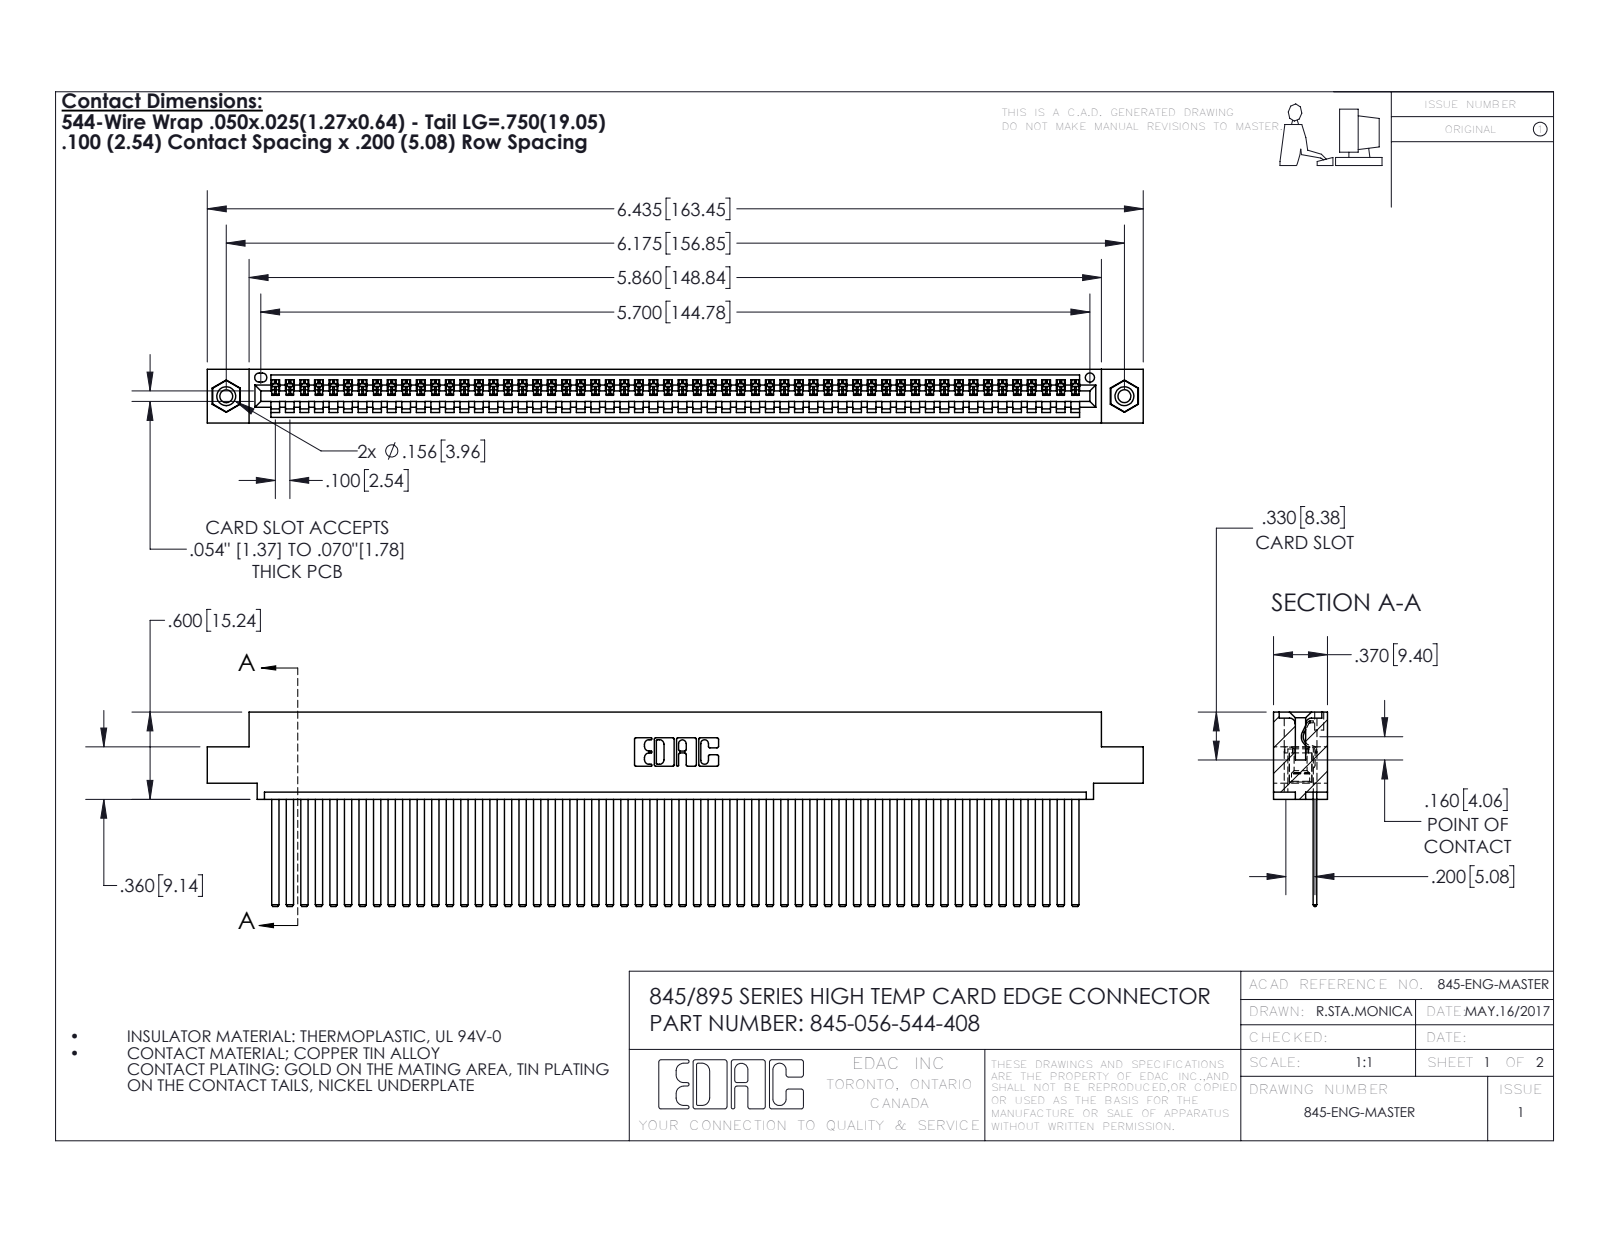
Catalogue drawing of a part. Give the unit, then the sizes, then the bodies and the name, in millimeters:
Units: millimetres
Overall size (bounding box): 163.4 × 34 × 9.4
Round holes (diameter × count): ⌀2.3 ×2, ⌀3.2 ×2, ⌀4 ×2, ⌀1.6 ×1
Round bosses / shafts (diameter × count): ⌀3.9 ×2
Partial cylindrical surfaces — rounded edges, fillets, slot ends (radius × count): R0.2 ×112, R0.3 ×22, R0.2 ×6, R0.8 ×6, R0.7 ×3, R0.8 ×2, R1 ×2, R0.4 ×1
Main face-to-face distances: 1.8, 7.6, 0.6, 2.5, 6.9, 9.4, 5.1, 5.7, 3.8, 1.8
Hole centre spacings: 6.9, 150.9, 156.8
Volume: 16 200 mm³ · Surface area: 23 770 mm²
Bodies: 59 solids, 3102 faces (2132 planar, 954 cylindrical, 16 other)
Part name (STEP PRODUCT): 345 Part_0.110 Offset - 0.156 Dia-TI; 345-056-544-408; 345-292-001_345-293-144; 345-250-001_345-250-003-102
STEP written by: SolidWorks 2016 (CONFIG_CONTROL_DESIGN)
